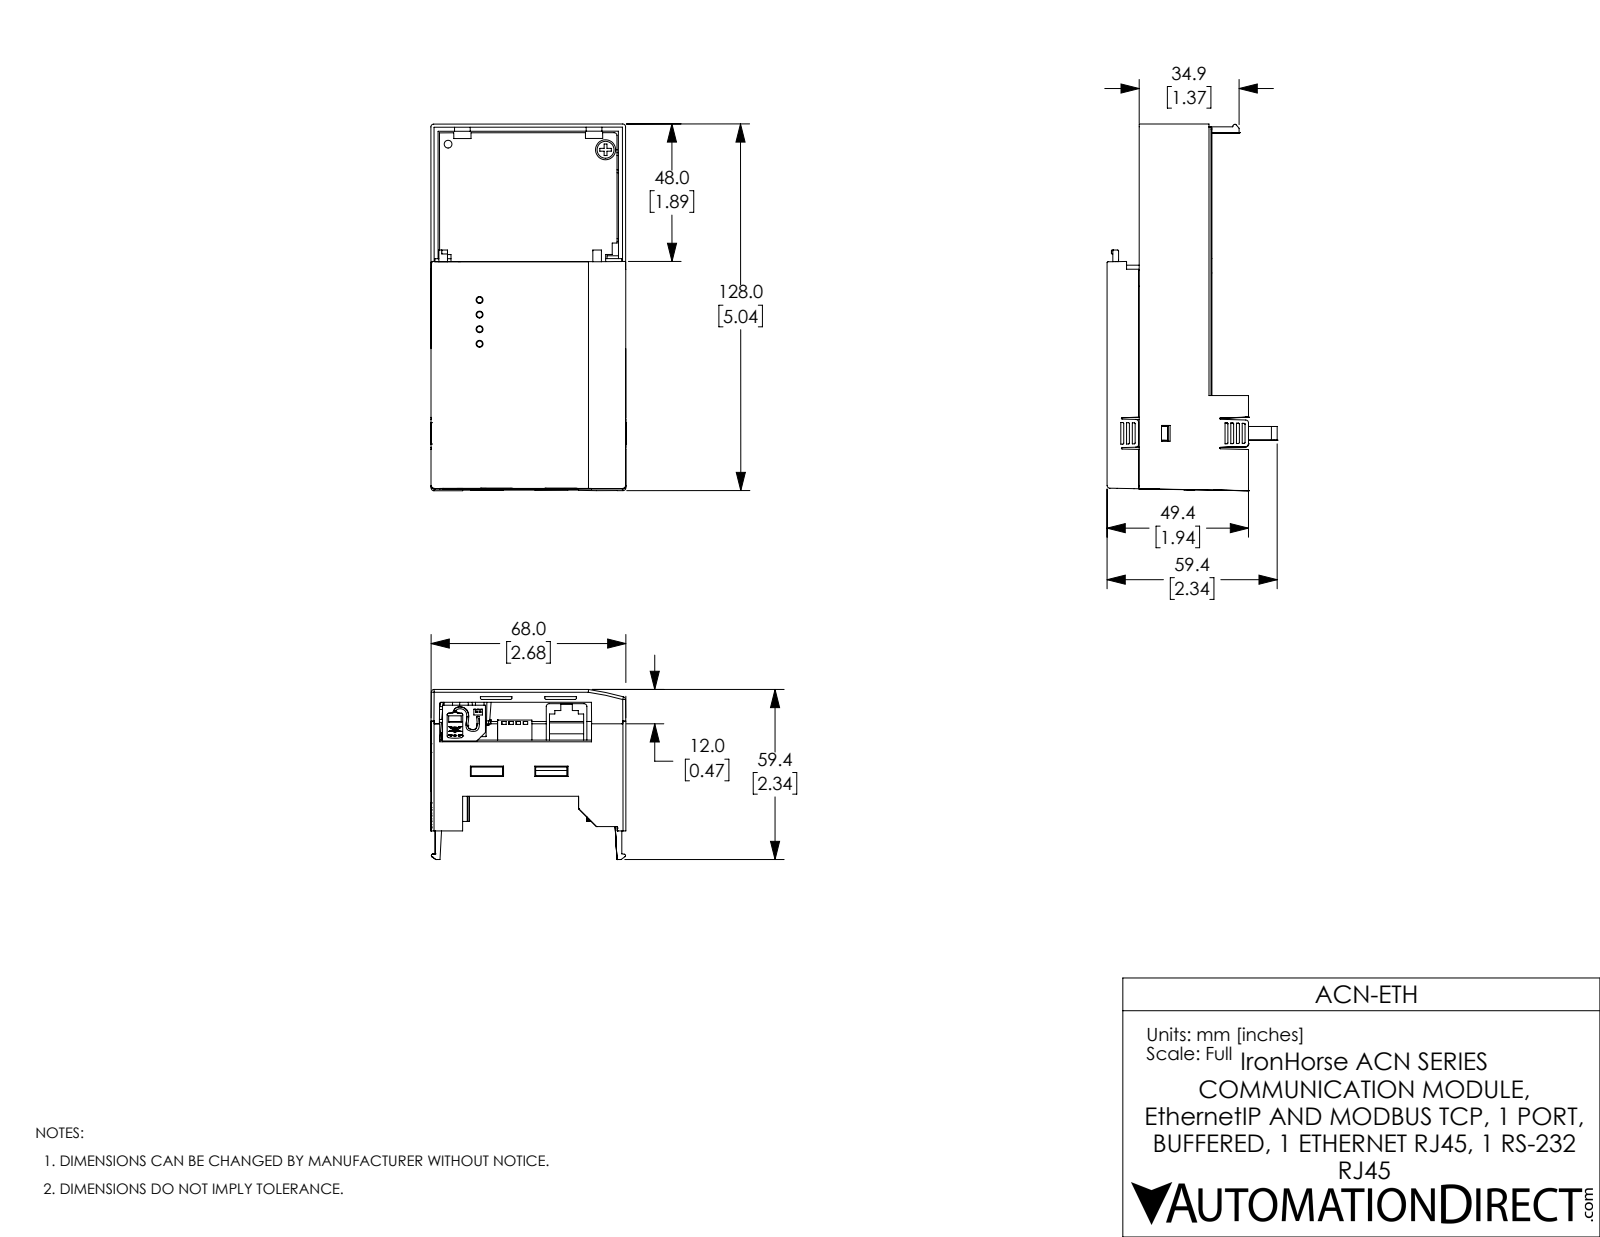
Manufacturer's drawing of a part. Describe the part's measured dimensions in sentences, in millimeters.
The part is named "S100_OPTION_MODULE_ETHERNET_200525 Mod r1C fXT". Its 3-D file was written by "SolidWorks 2017 (AUTOMOTIVE_DESIGN)". It is 10 solids with 1626 faces: 1132 planar, 356 cylindrical and 138 other. Overall it measures 128 by 68.1 by 59.4 millimeters. Its volume is 77 150 cubic millimeters and its surface area 78 840 square millimeters. Round holes: 4 of diameter 0.9, 2 of diameter 2.5, 2 of diameter 3.5. Round bosses or shafts: 4 of diameter 2.5, 4 of diameter 0.8, 2 of diameter 8, 2 of diameter 7, 2 of diameter 5.9, 2 of diameter 3, 1 of diameter 2.7, 1 of diameter 0.8. Partial cylindrical surfaces (rounded edges, fillets, slot ends): 54 of radius 1, 45 of radius 0.3, 19 of radius 0.5, 8 of radius 0.2, 8 of radius 0.7, 6 of radius 0.1, 6 of radius 0.3, 6 of radius 1.9. The main face-to-face distances are 2.5, 22.3, 1.6, 3, 4.6, 7.1, 5.5, 65.5, 24.8, 19.3. The hole center spacings are 5.1, 10.2, 15.3, 59.1, 62.9, 66.7, 66.9, 70.8.
